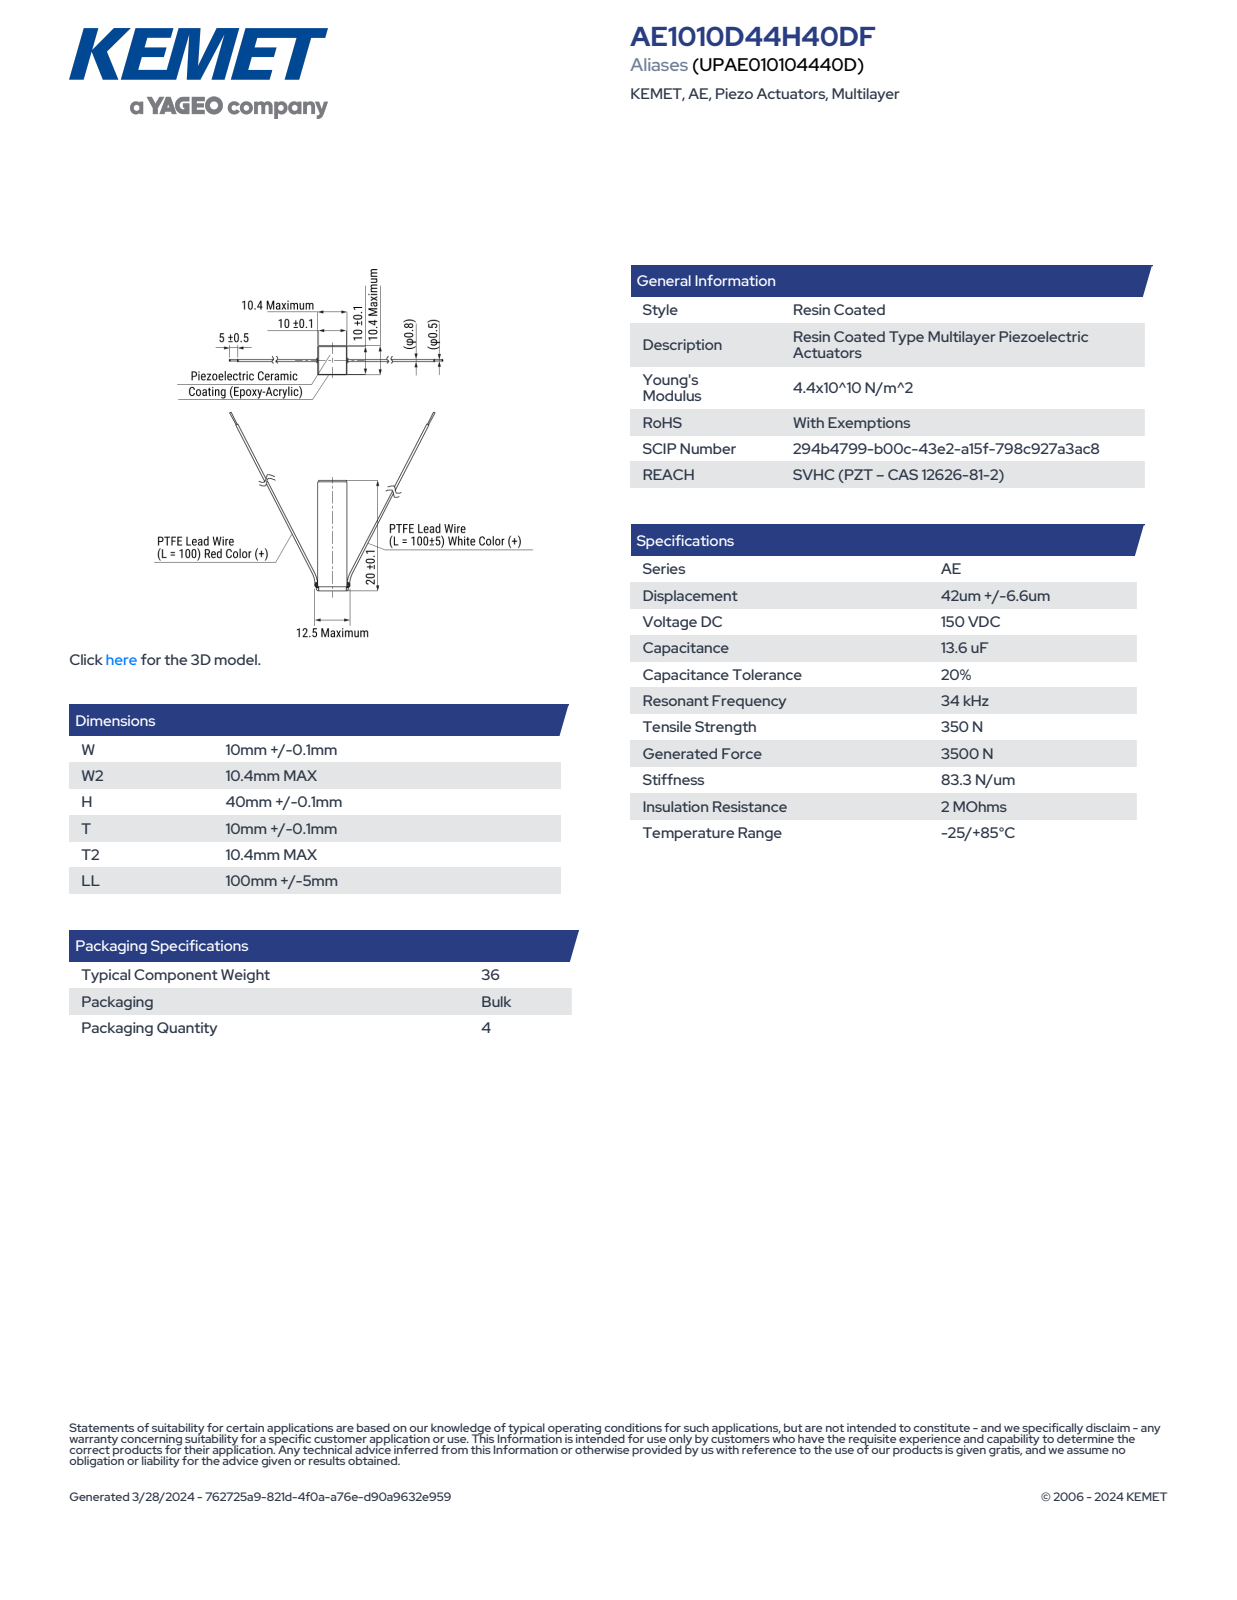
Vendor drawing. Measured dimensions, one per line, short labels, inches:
name: AL_KAE2_W10.1W210.4H40.1T10.1T210.4
written by: SolidWorks 2020 (AUTOMOTIVE_DESIGN)
unit: in
bodies: 4 solids, 93 faces (85 planar, 8 cylindrical, 0 other)
size: 1.579 × 0.409 × 0.409
volume: 0.25 in³; area: 2.886 in²
rounds: 8× R0.006
face distances: 0.398, 0.404, 0.394, 0.39, 0.409, 1.579, 0.635, 0.944, 0.155, 1.424
